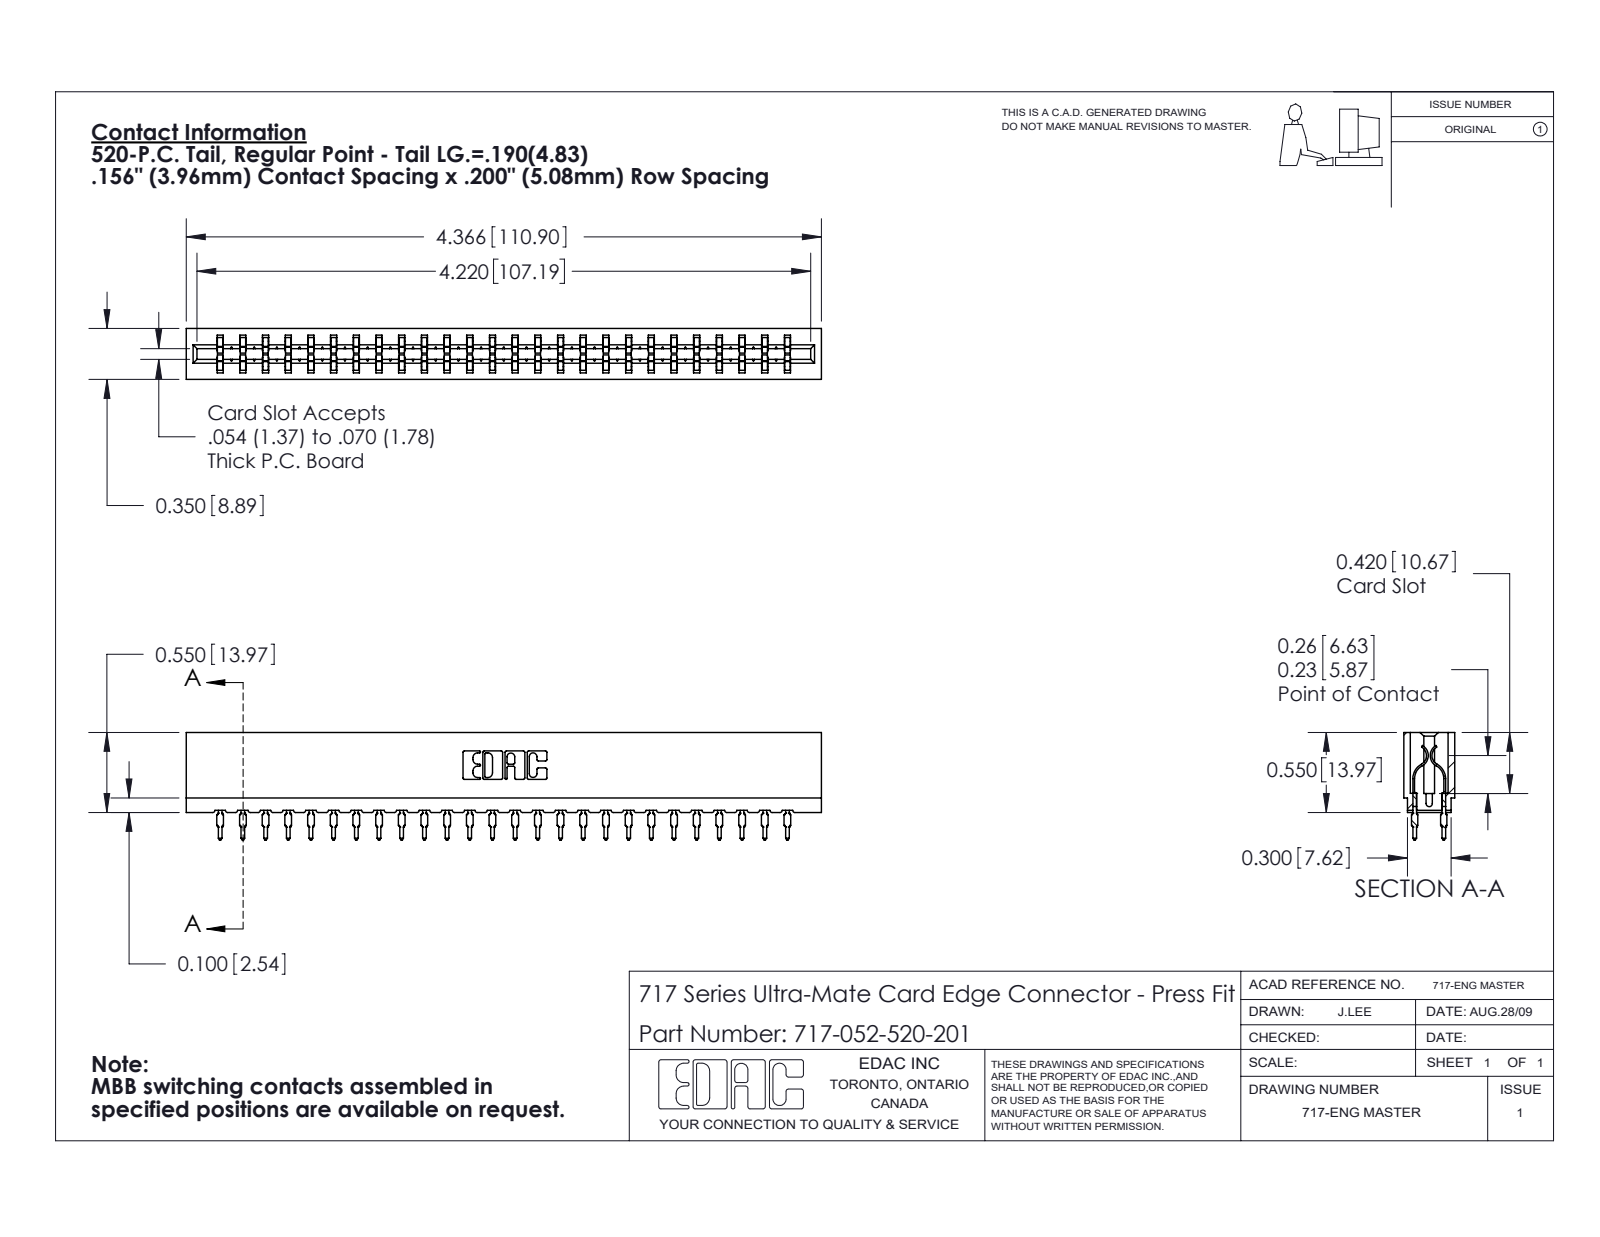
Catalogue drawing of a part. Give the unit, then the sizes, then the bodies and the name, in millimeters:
Units: millimetres
Overall size (bounding box): 110.9 × 18.8 × 8.9
Partial cylindrical surfaces — rounded edges, fillets, slot ends (radius × count): R0.5 ×104, R0.4 ×52, R0.3 ×22, R0.1 ×8, R0.3 ×8, R0.2 ×6, R0.8 ×6, R0.7 ×3
Main face-to-face distances: 5.4, 3.5, 8.9, 1.6, 7.3, 1.9, 3.8, 4, 1.9, 1.1
Volume: 9 640 mm³ · Surface area: 14 260 mm²
Bodies: 53 solids, 4774 faces (2472 planar, 950 cylindrical, 1352 other)
Part name (STEP PRODUCT): 745-292-001_520; 717-052-520-201; 717 Part_Insulator Option - 06
STEP written by: SolidWorks 2020 (CONFIG_CONTROL_DESIGN)
